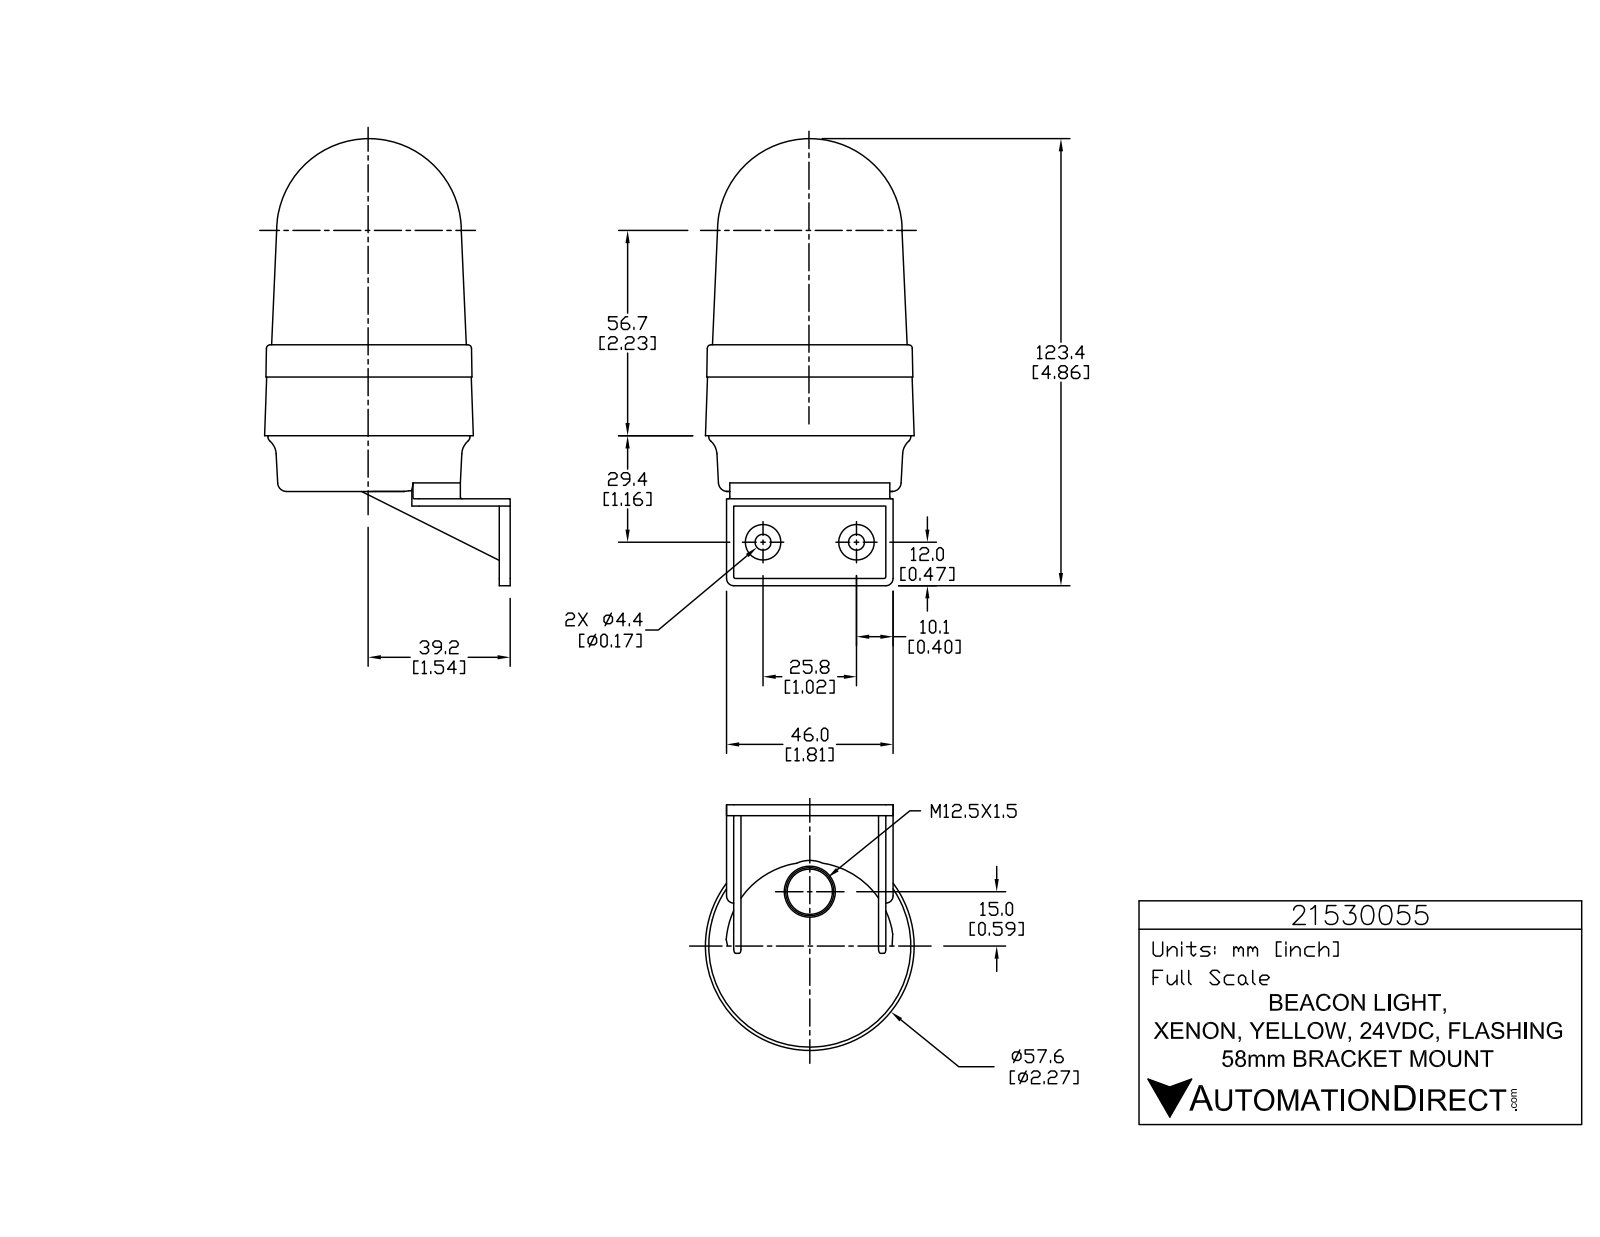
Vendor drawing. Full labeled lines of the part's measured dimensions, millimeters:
Part name (STEP PRODUCT): 21530055
STEP written by: SolidWorks 2015 (AUTOMOTIVE_DESIGN)
Units: millimetres
Bodies: 1 solid, 828 faces (551 planar, 179 cylindrical, 98 other)
Overall size (bounding box): 123.4 × 72.4 × 61.1
Volume: 203 700 mm³ · Surface area: 24 190 mm²
Round holes (diameter × count): ⌀1 ×3, ⌀4.4 ×2
Round bosses / shafts (diameter × count): ⌀5.7 ×3, ⌀1.4 ×3, ⌀9.8 ×2, ⌀55.8 ×1
Partial cylindrical surfaces — rounded edges, fillets, slot ends (radius × count): R0.2 ×6, R0.2 ×6, R0.2 ×6, R0.5 ×6, R3.3 ×6, R2 ×4, R0.1 ×3, R0.1 ×3
Main face-to-face distances: 2, 4, 40, 42, 1, 3, 38, 22, 24, 19.4
Hole centre spacings: 25.8
